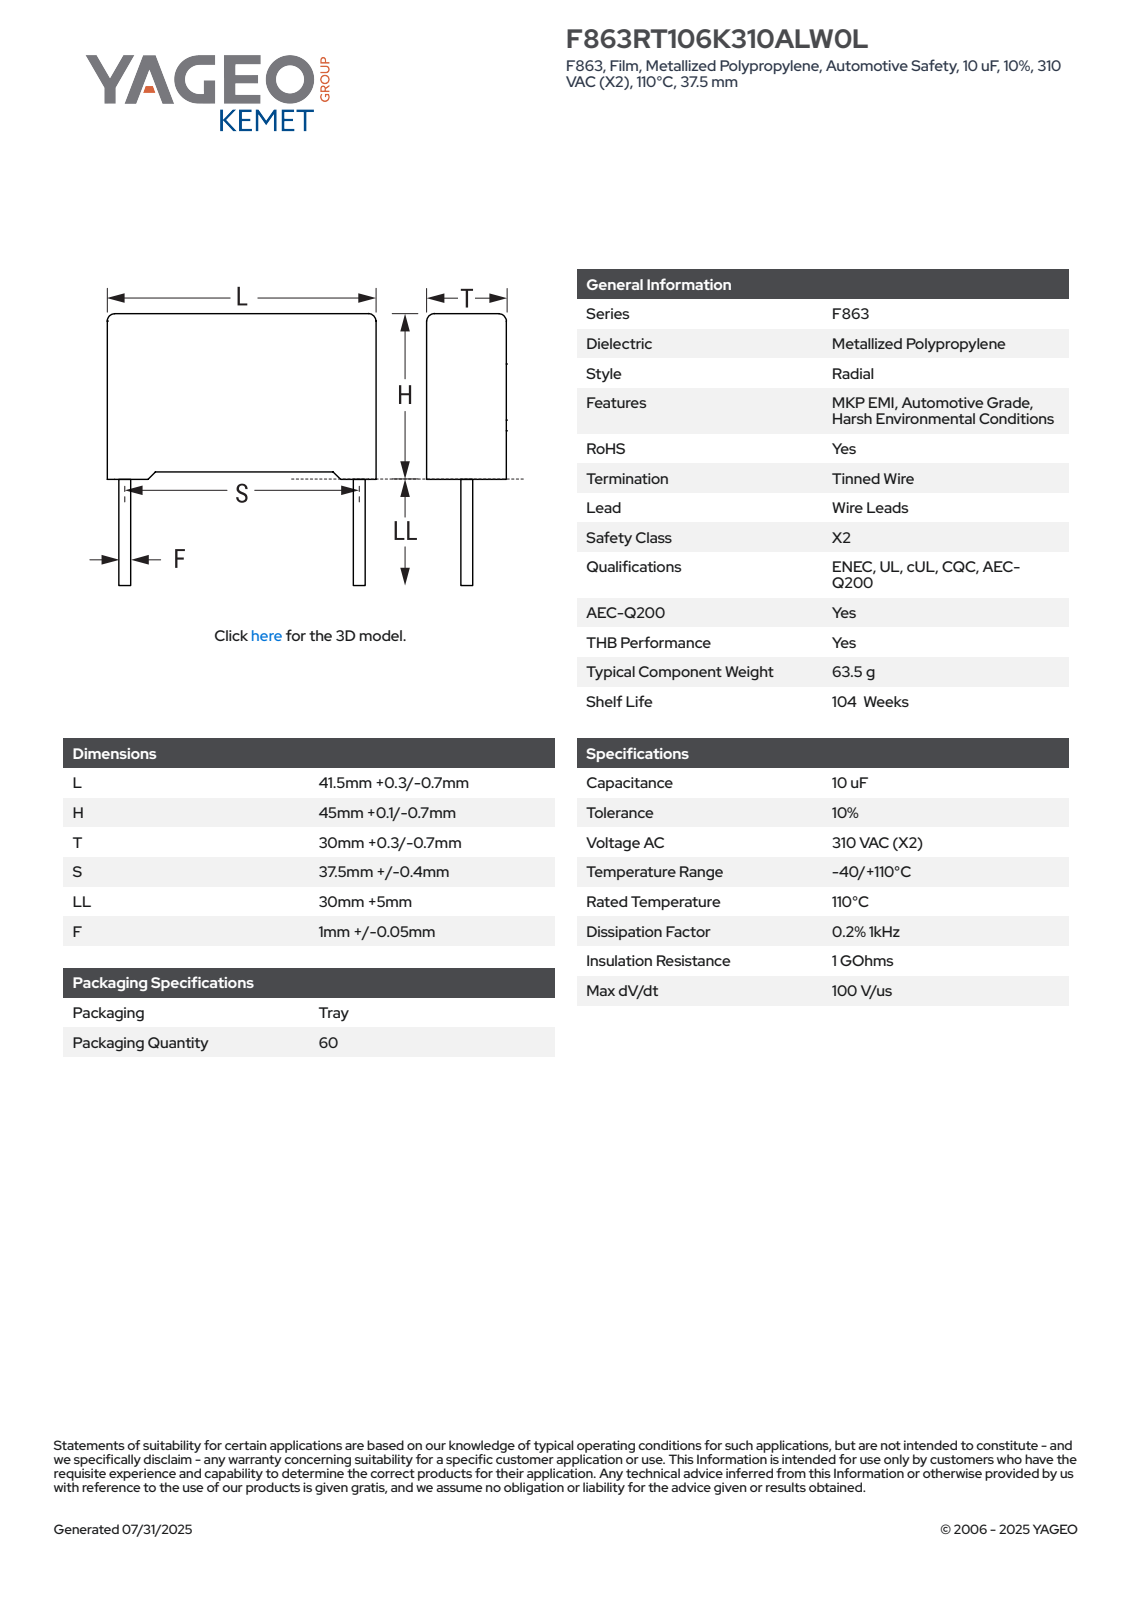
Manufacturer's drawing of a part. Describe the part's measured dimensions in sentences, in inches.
The part is named "CFR_RB2_41.5X45X30_L41.8H45.1T30.3S37.5LL35F1.05". Its 3-D file was written by "SolidWorks 2021 (AUTOMOTIVE_DESIGN)". It is 4 solids with 85 faces: 77 planar, 8 cylindrical and 0 other. Overall it measures 3.154 by 1.646 by 1.193 inches. Its volume is 3.387 cubic inches and its surface area 14.48 square inches. Round bosses or shafts: 2 of diameter 0.041. Partial cylindrical surfaces (rounded edges, fillets, slot ends): 4 of radius 0.02. The main face-to-face distances are 1.193, 1.646, 1.714, 0.032, 1.746, 0.03, 0.061, 1.776, 0.055, 1.591.
